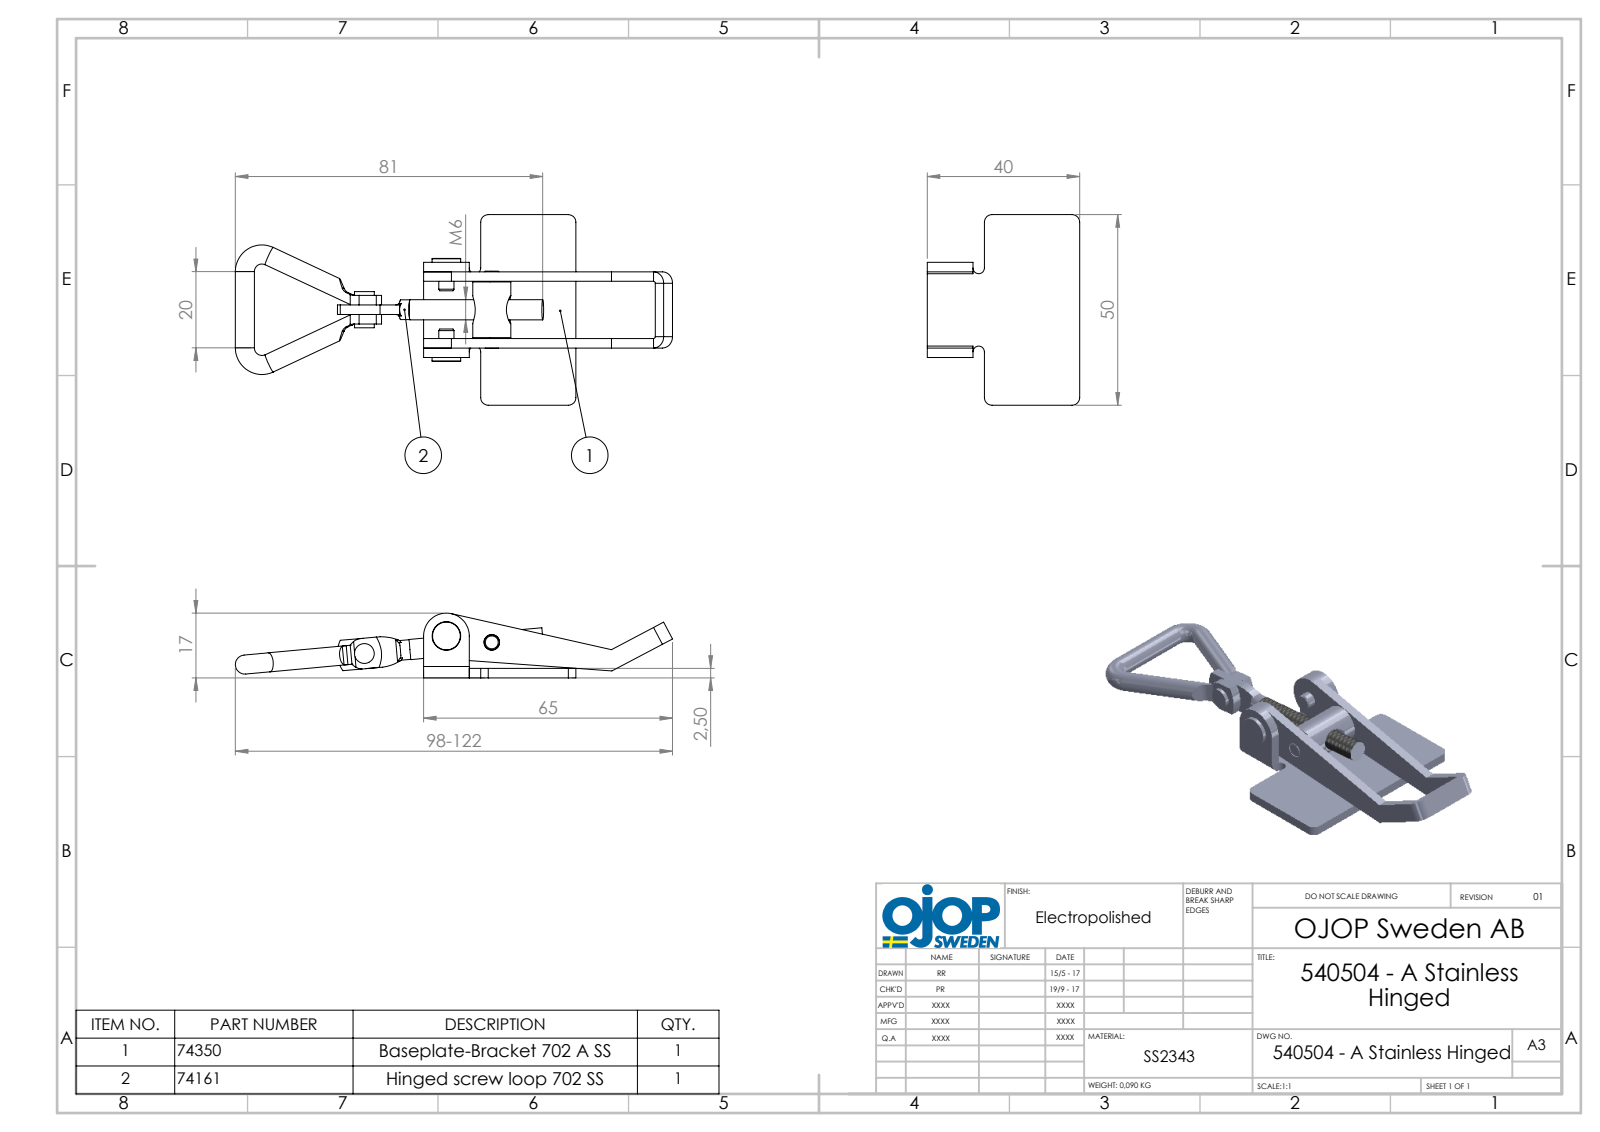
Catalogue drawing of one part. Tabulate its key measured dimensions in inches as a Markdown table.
| quantity | value |
| --- | --- |
| part name | 702 - Ring till ledad M6; 702 - Ring 702 M6; 702 - Skruv till ledad M6; 702 - Nit till ledad M6 (+5 more) |
| STEP written by | SolidWorks 2015 (AUTOMOTIVE_DESIGN) |
| units | inches |
| bodies | 8 solids, 201 faces (82 planar, 97 cylindrical, 22 other) |
| overall size | 4.655 × 1.969 × 0.669 |
| volume | 0.721 in³ |
| surface area | 17.9 in² |
| round holes (diameter × count) | 0.161 × 3, 0.197 × 2 |
| round bosses / shafts (diameter × count) | 0.197 × 3, 0.157 × 2, 0.394 × 1, 0.295 × 1, 0.236 × 1, 0.209 × 1, 0.205 × 1, 0.204 × 1 |
| partial cylindrical surfaces (radius × count) | 0.079 × 8, 0.039 × 6, 0.02 × 4, 0.118 × 4, 0.059 × 2, 0.267 × 2, 0.485 × 2, 0.152 × 1 |
| main face-to-face distances | 0.098, 0.689, 0.787, 0.591, 0.197, 0.343, 0.346, 0.441, 0.445, 0.886 |
| hole center spacings | 0.474, 0.998, 1.456 |
